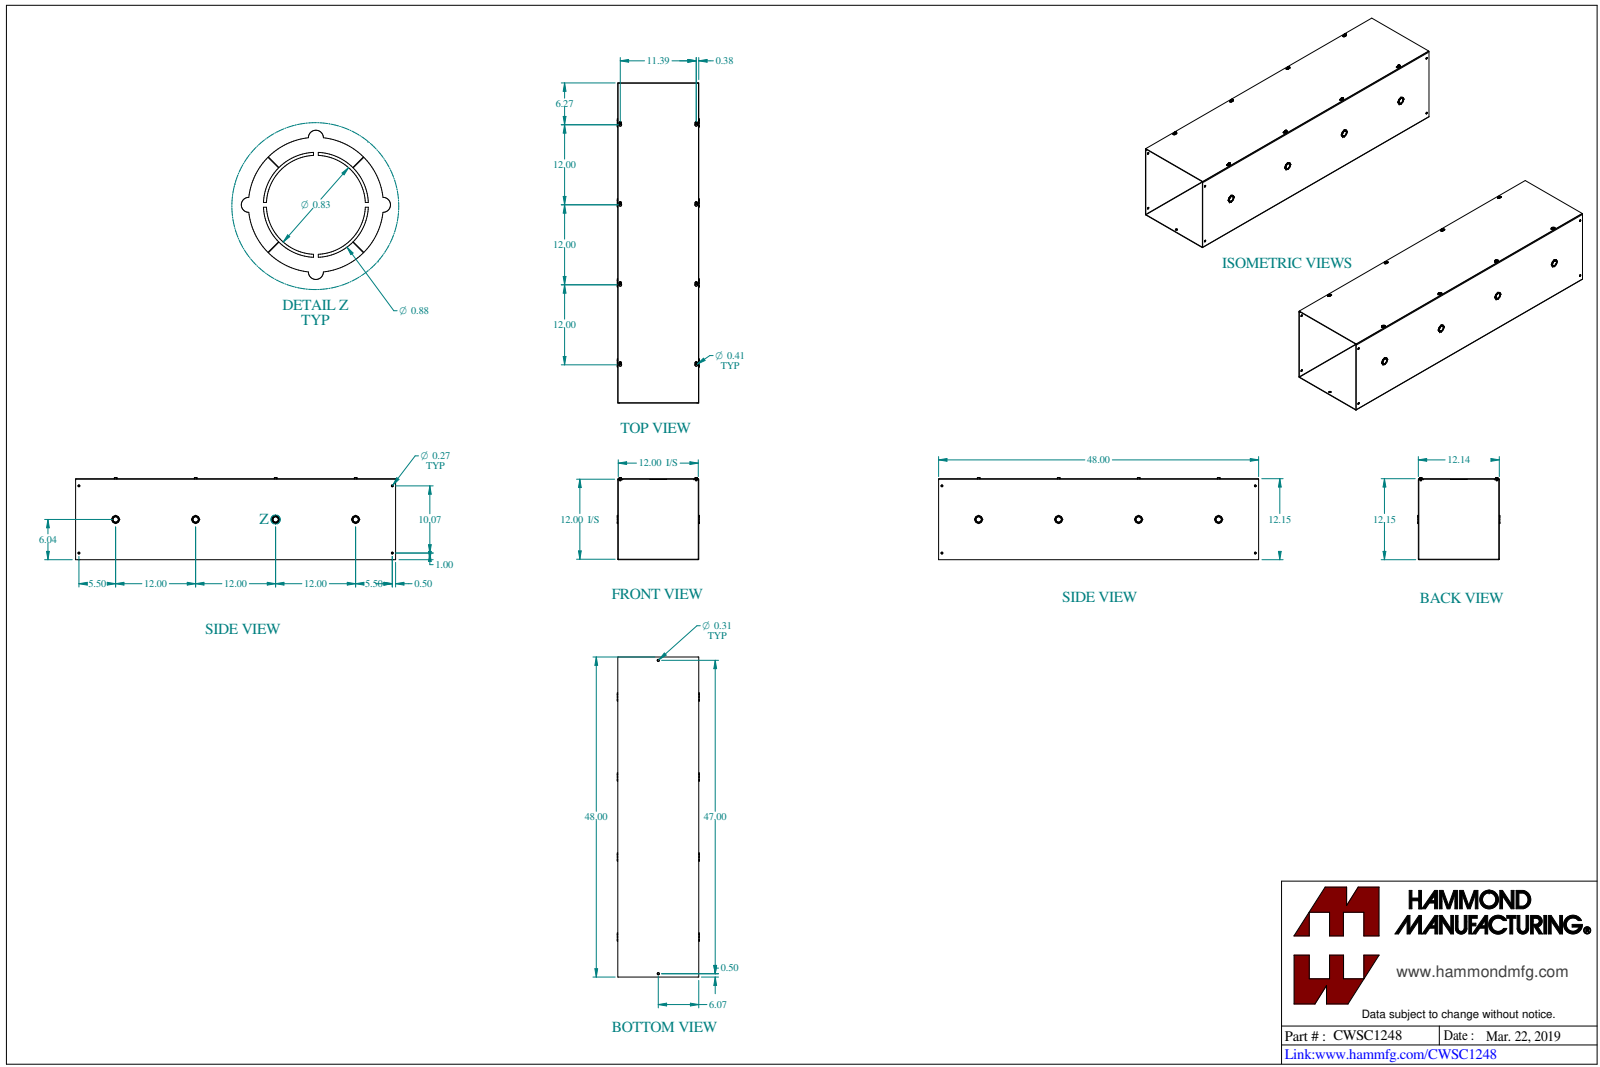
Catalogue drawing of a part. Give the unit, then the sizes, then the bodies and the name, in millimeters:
Units: millimetres
Overall size (bounding box): 1219.2 × 313.1 × 312.1
Round holes (diameter × count): ⌀4.5 ×8, ⌀6.8 ×4, ⌀22.2 ×4, ⌀8 ×2
Round bosses / shafts (diameter × count): ⌀9.5 ×8, ⌀4.8 ×8, ⌀28.6 ×4, ⌀21 ×4
Partial cylindrical surfaces — rounded edges, fillets, slot ends (radius × count): R1.6 ×16, R3.2 ×8, R5.2 ×8, R0.9 ×4, R2.7 ×4
Main face-to-face distances: 1.8, 306.6, 304.8, 2, 308.5, 308.6, 306.8, 303, 3.8, 0.8
Hole centre spacings: 304.8, 420.3, 609.6, 201.1, 289.4, 462.5, 467.5, 674.8
Volume: 2 864 000 mm³ · Surface area: 3 079 000 mm²
Bodies: 10 solids, 640 faces (284 planar, 308 cylindrical, 48 other)
Part name (STEP PRODUCT): CWSC1248
STEP written by: SolidWorks 2023 (CONFIG_CONTROL_DESIGN)
